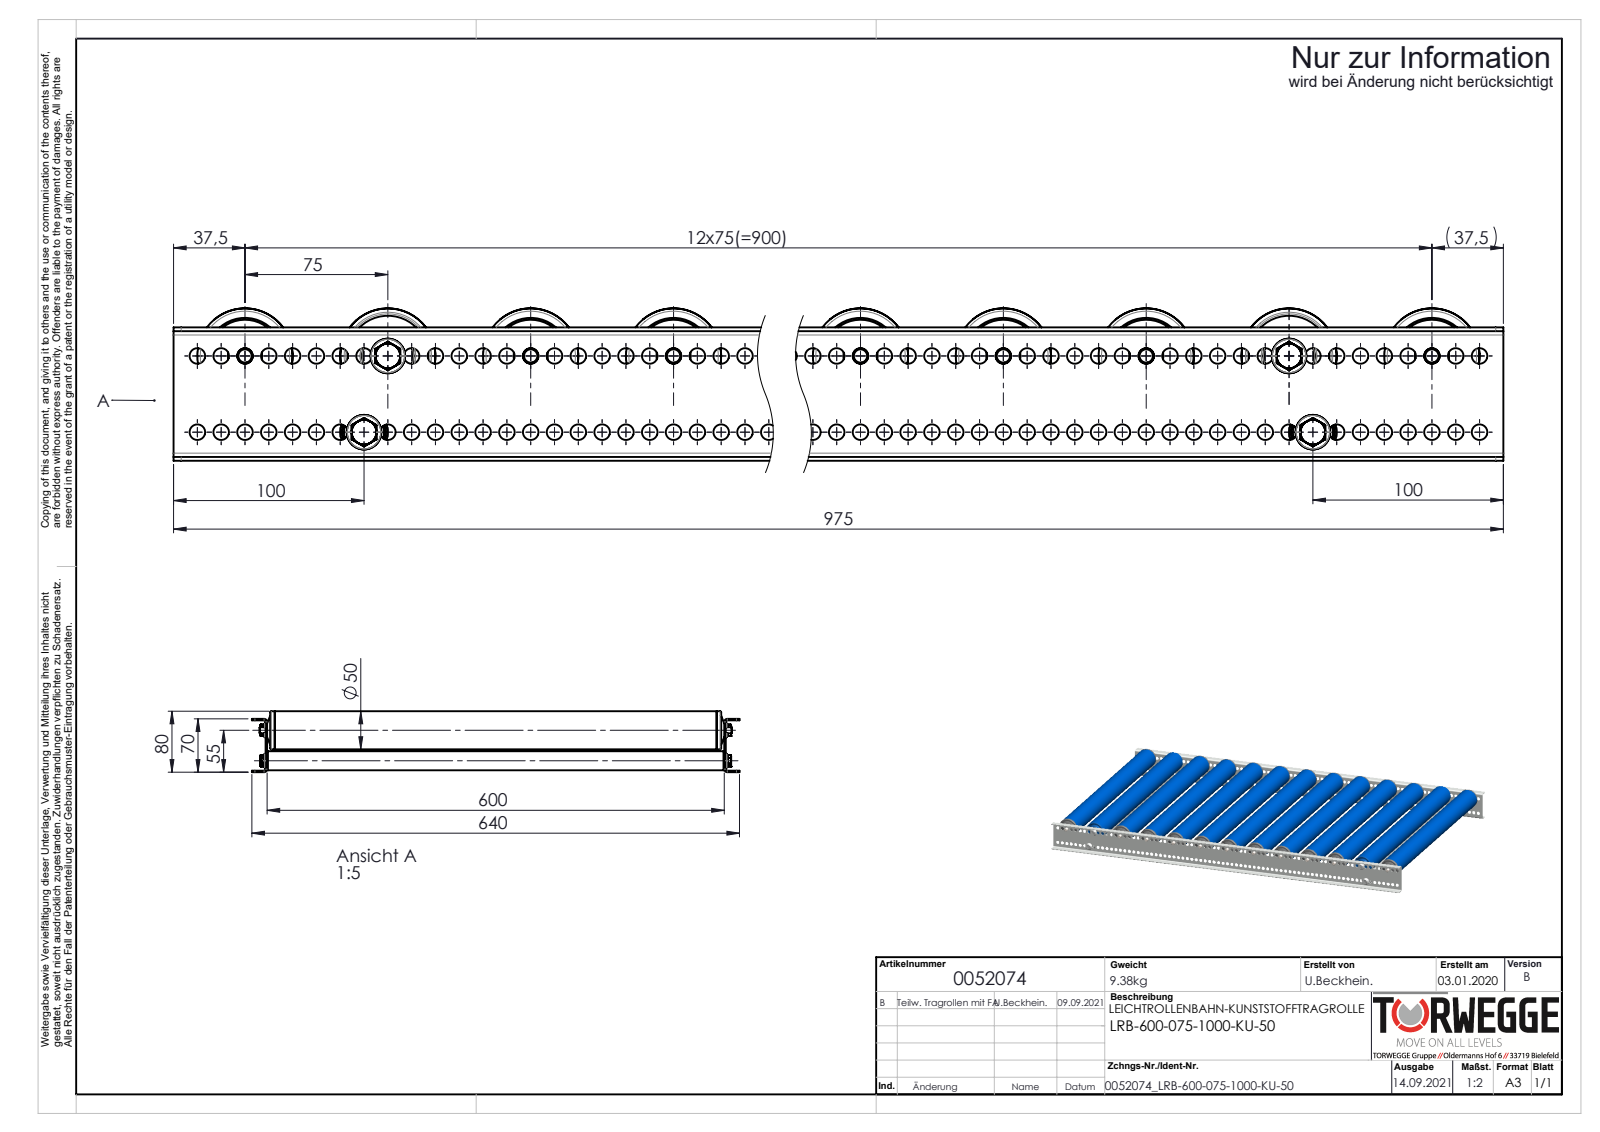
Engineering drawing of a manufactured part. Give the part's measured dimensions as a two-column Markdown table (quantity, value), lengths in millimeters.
| quantity | value |
| --- | --- |
| part name | 0017015_Tragrollenrohr-Ø50x2,8KU_KFG_L=580; 0026266_Typ-KUT100-50x2,8-12; 0039780-Achse-ST-Ø12-KFG_IGM8-AL=600; KUT100-50x2,8-KB-A12-IGM8-EL=KFG_S100914_KUT100-50x2,8-KB-A12-IGM8-EL=600 (+8 more) |
| STEP written by | SolidWorks 2020 (AUTOMOTIVE_DESIGN) |
| units | millimeters |
| bodies | 241 solids, 4494 faces (1180 planar, 1912 cylindrical, 1402 other) |
| overall size | 975 × 640 × 80 |
| volume | 4 878 000 mm³ |
| surface area | 3 586 000 mm² |
| round holes (diameter × count) | 8.2 × 154, 7.6 × 11, 8 × 11, 25 × 11, 30 × 11, 35 × 11, 39.4 × 11, 40 × 11, 6.8 × 4, 12 × 2, 12.1 × 2, 16 × 2 |
| round bosses / shafts (diameter × count) | 50 × 13, 44.4 × 11, 38 × 11, 36 × 11, 33 × 11, 22 × 11, 21 × 11, 25 × 4 |
| partial cylindrical surfaces (radius × count) | 0.6 × 22, 0.75 × 22, 2.45 × 22, 4.87 × 11, 7 × 11, 4 × 8, 2 × 4, 2.5 × 4 |
| main face-to-face distances | 2, 602, 68, 600, 604, 66, 70, 592, 6, 12 |
| hole center spacings | 12.5, 25, 37.5, 50, 62.5, 75, 87.5, 100 |
